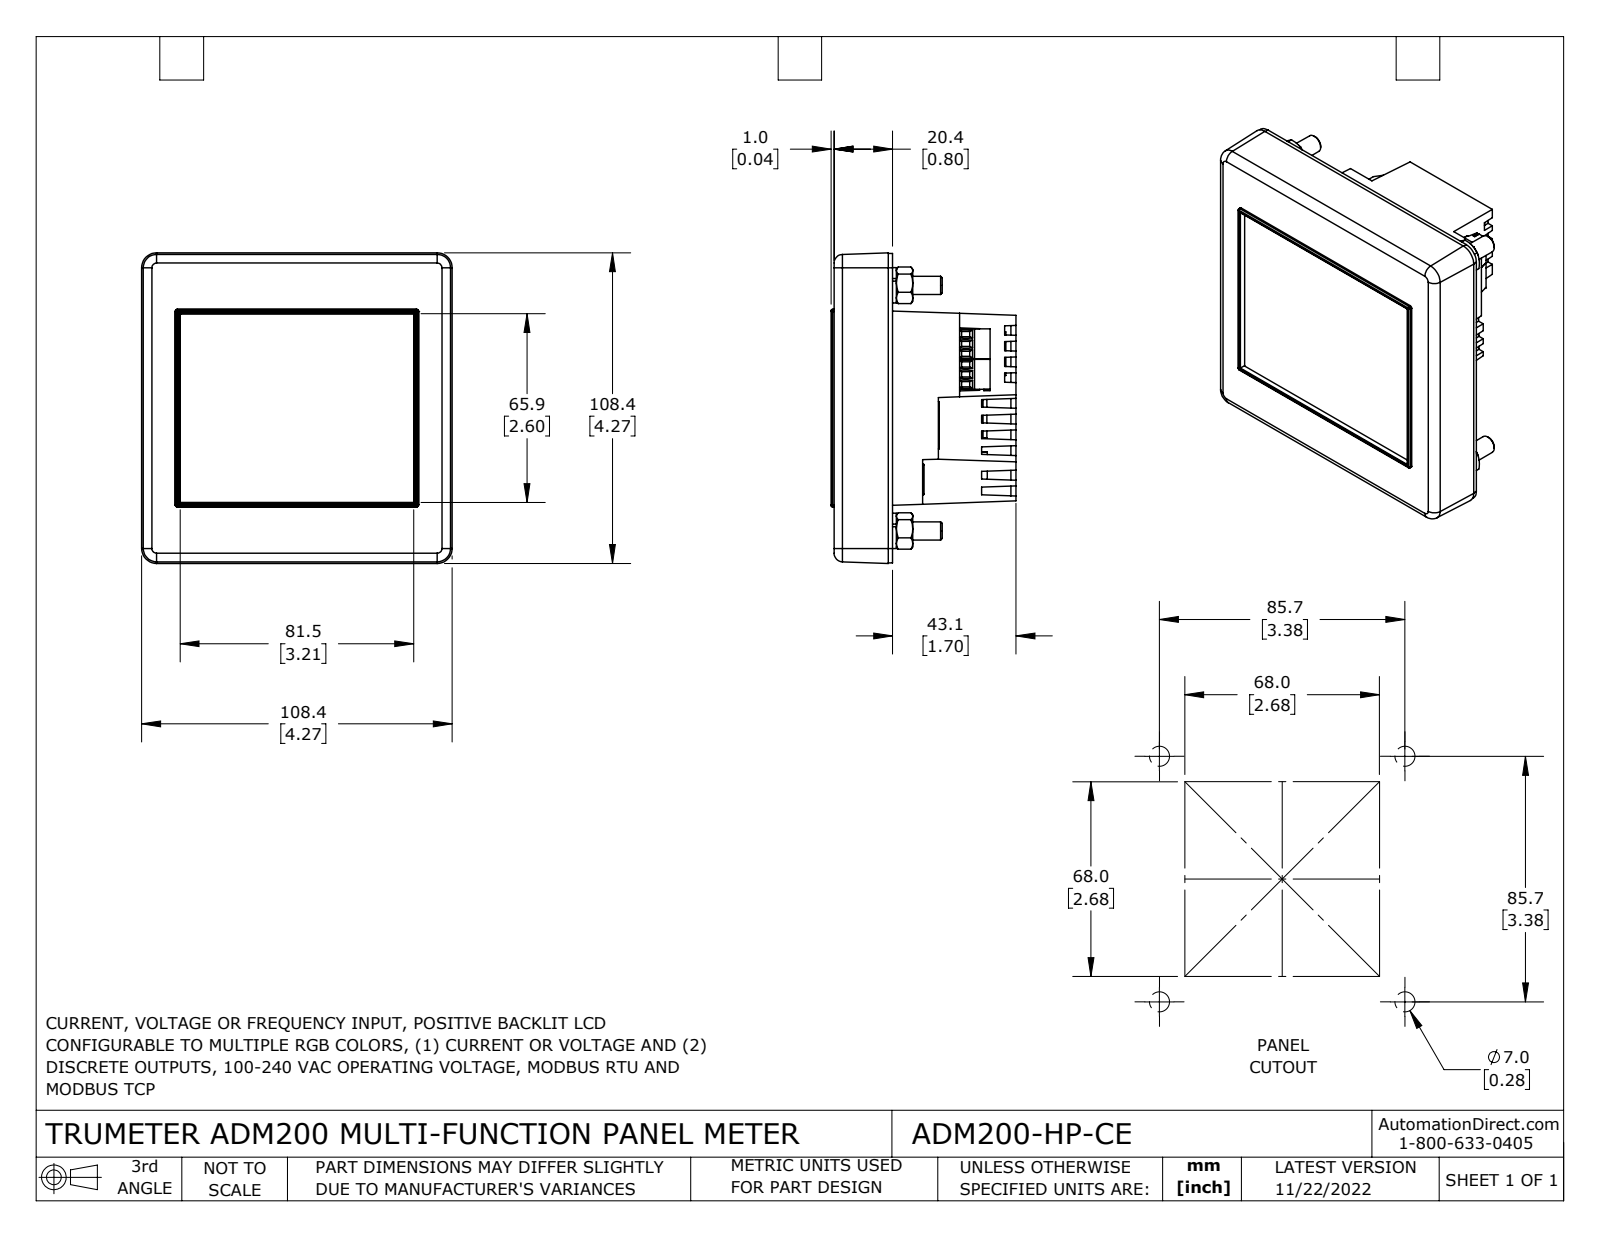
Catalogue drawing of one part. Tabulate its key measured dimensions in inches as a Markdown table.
| quantity | value |
| --- | --- |
| part name | ADM200-HP-CE |
| STEP written by | SolidWorks 2021 (CONFIG_CONTROL_DESIGN) |
| units | inches |
| bodies | 23 solids, 2059 faces (1384 planar, 290 cylindrical, 385 other) |
| overall size | 4.269 × 4.269 × 2.541 |
| volume | 7.808 in³ |
| surface area | 190.8 in² |
| round holes (diameter × count) | 0.071 × 9, 0.114 × 6, 0.118 × 5, 0.213 × 4, 0.25 × 4, 0.26 × 4, 0.295 × 4, 0.154 × 2 |
| round bosses / shafts (diameter × count) | 0.039 × 5, 0.487 × 4, 0.438 × 4, 0.024 × 4, 0.079 × 2 |
| partial cylindrical surfaces (radius × count) | 0.006 × 32, 0.02 × 30, 0.039 × 7, 0.016 × 4, 0.03 × 4, 0.118 × 4, 0.197 × 4, 0.004 × 2 |
| main face-to-face distances | 0.031, 0.635, 0.11, 0.073, 0.059, 0.079, 0.694, 3.395, 3.468, 0.047 |
| hole center spacings | 0.709, 3.228, 0.136, 0.293, 0.986, 1.417, 2.126, 2.399 |
